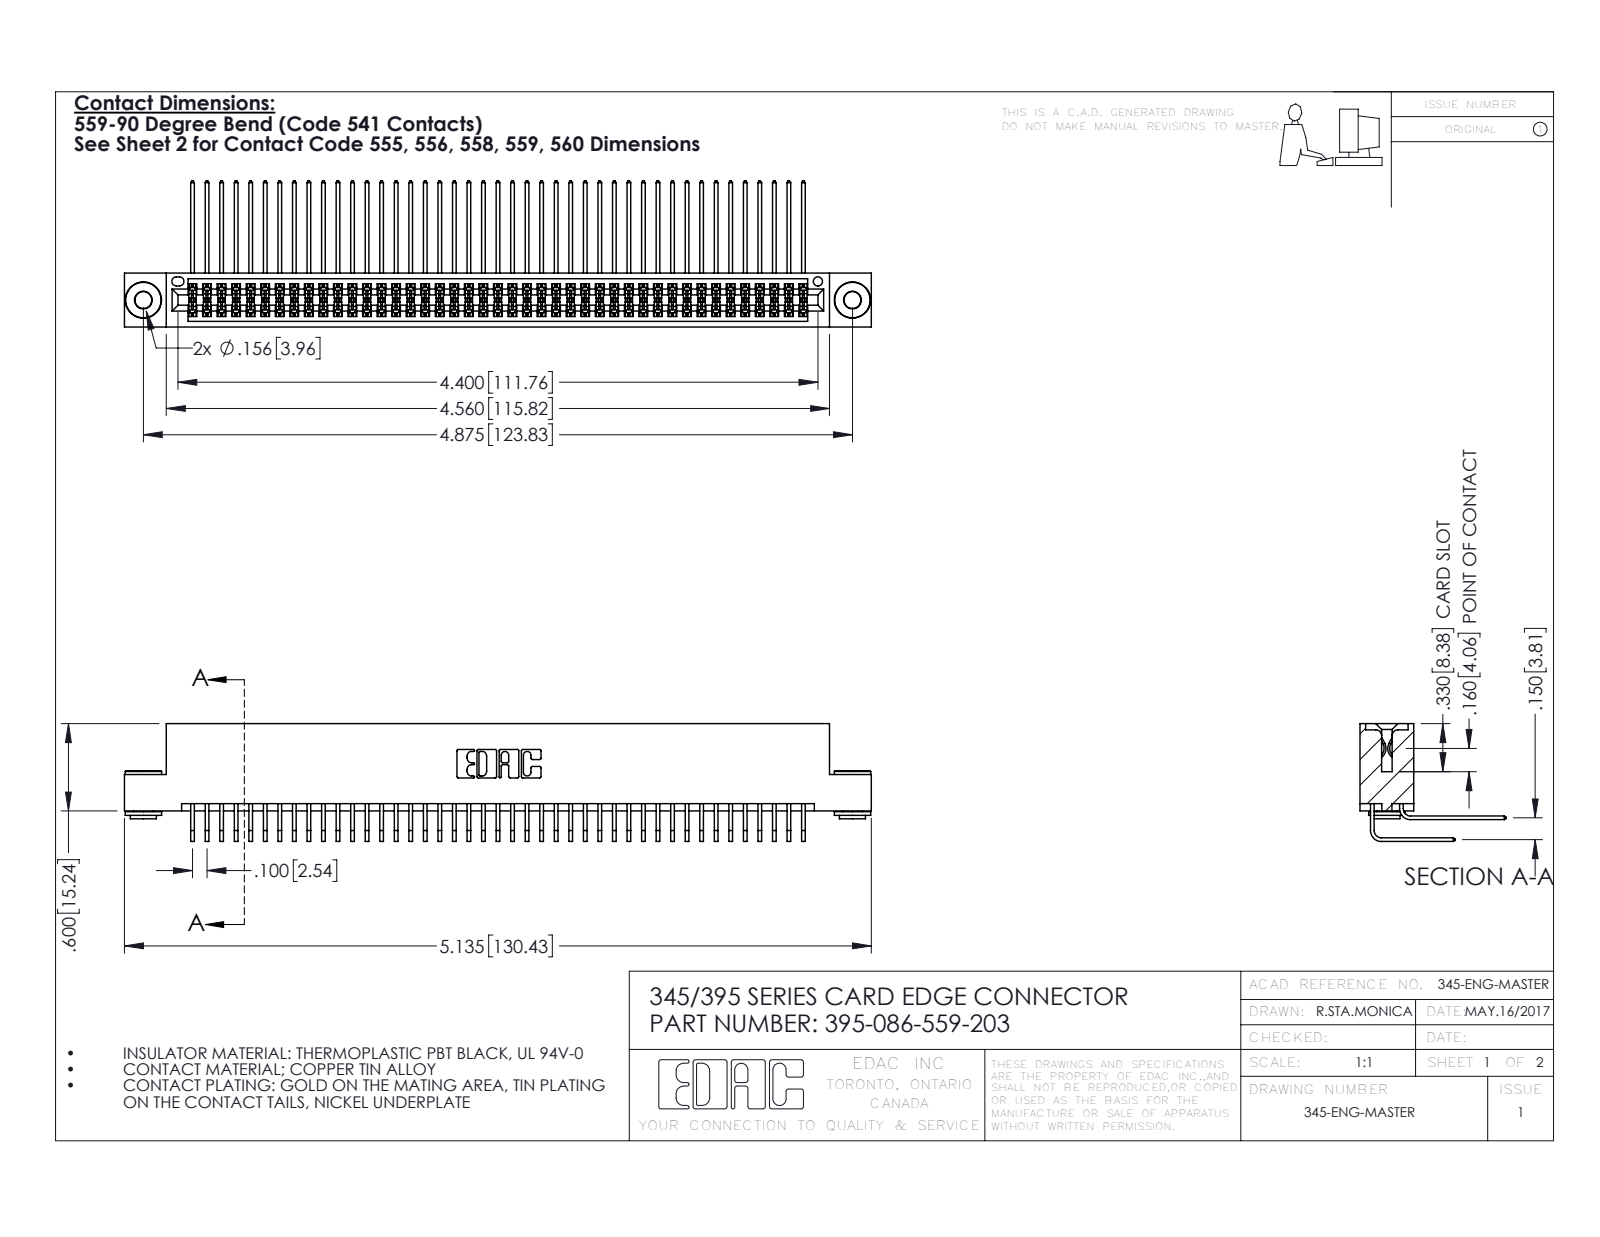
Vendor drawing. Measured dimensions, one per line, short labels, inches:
name: 345-250-002_345-250-002-102; 345-292-001_558 559 Tail - 1; 345 Part_Flush Mounting Lugs - 0.156 Dia-TH; 345-292-001_559 Tail - 2 (+1 more)
written by: SolidWorks 2016 (CONFIG_CONTROL_DESIGN)
unit: in
bodies: 89 solids, 4636 faces (3100 planar, 1528 cylindrical, 8 other)
size: 5.135 × 1.005 × 0.809
volume: 0.805 in³; area: 34.2 in²
holes: 2× ⌀0.116, 2× ⌀0.156, 1× ⌀0.064
bosses: 2× ⌀0.25, 2× ⌀0.18, 2× ⌀0.136
rounds: 130× R0.006, 22× R0.01, 6× R0.007, 6× R0.031, 3× R0.026, 2× R0.014, 2× R0.019, 2× R0.022
face distances: 0.072, 0.298, 0.2, 0.37, 0.025, 0.098, 0.272, 0.225, 0.175, 0.15
hole spacings: 0.27, 4.639, 4.875
